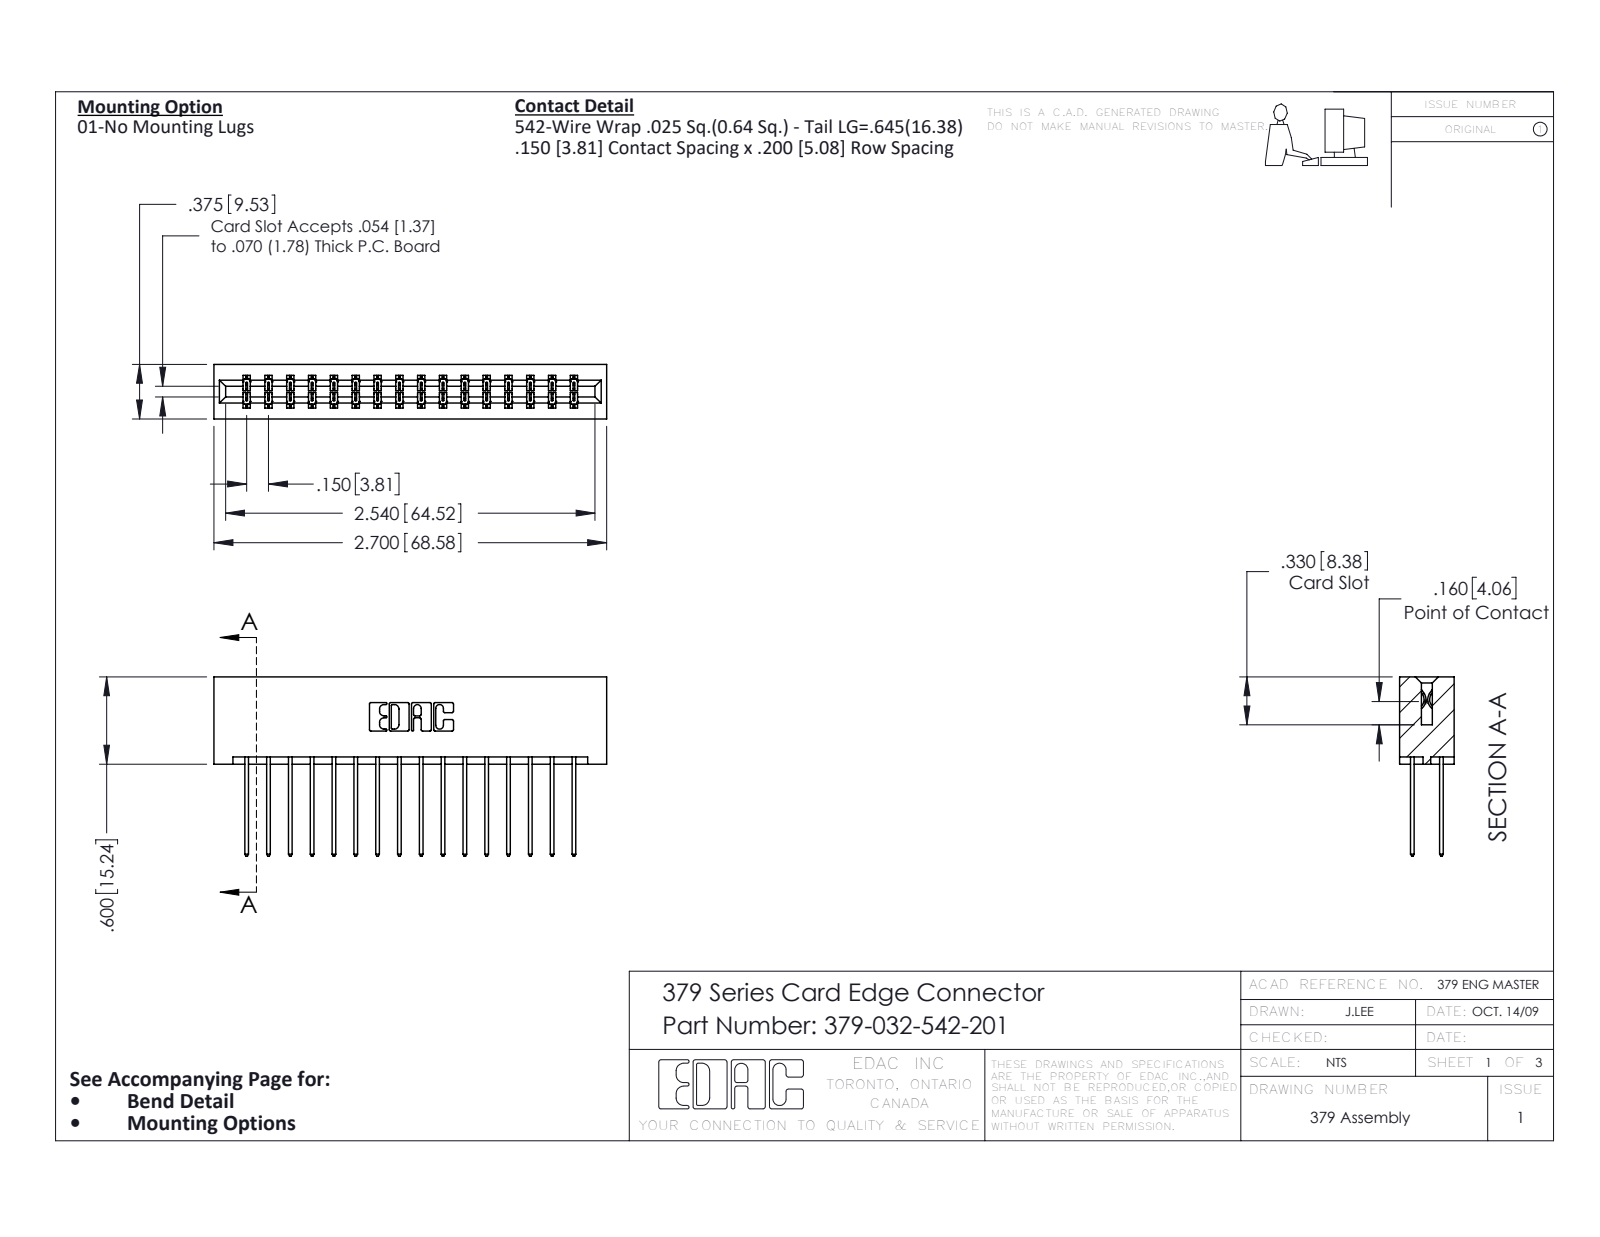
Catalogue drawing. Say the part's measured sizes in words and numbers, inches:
The part is named "379-032-542-201; 345-292-001_345-293-142; 379 Part_Lugless". Its 3-D file was written by "SolidWorks 2020 (CONFIG_CONTROL_DESIGN)". It is 33 solids with 1770 faces: 1218 planar, 552 cylindrical and 0 other. Overall it measures 2.7 by 1.232 by 0.375 inches. Its volume is 0.48 cubic inches and its surface area 14.55 square inches. Partial cylindrical surfaces (rounded edges, fillets, slot ends): 48 of radius 0.006, 32 of radius 0.01, 22 of radius 0.01, 6 of radius 0.007, 6 of radius 0.031, 3 of radius 0.026, 2 of radius 0.014, 2 of radius 0.022. The main face-to-face distances are 0.3, 0.075, 0.1, 0.2, 0.375, 0.15, 0.275, 0.025, 0.55, 0.15.
